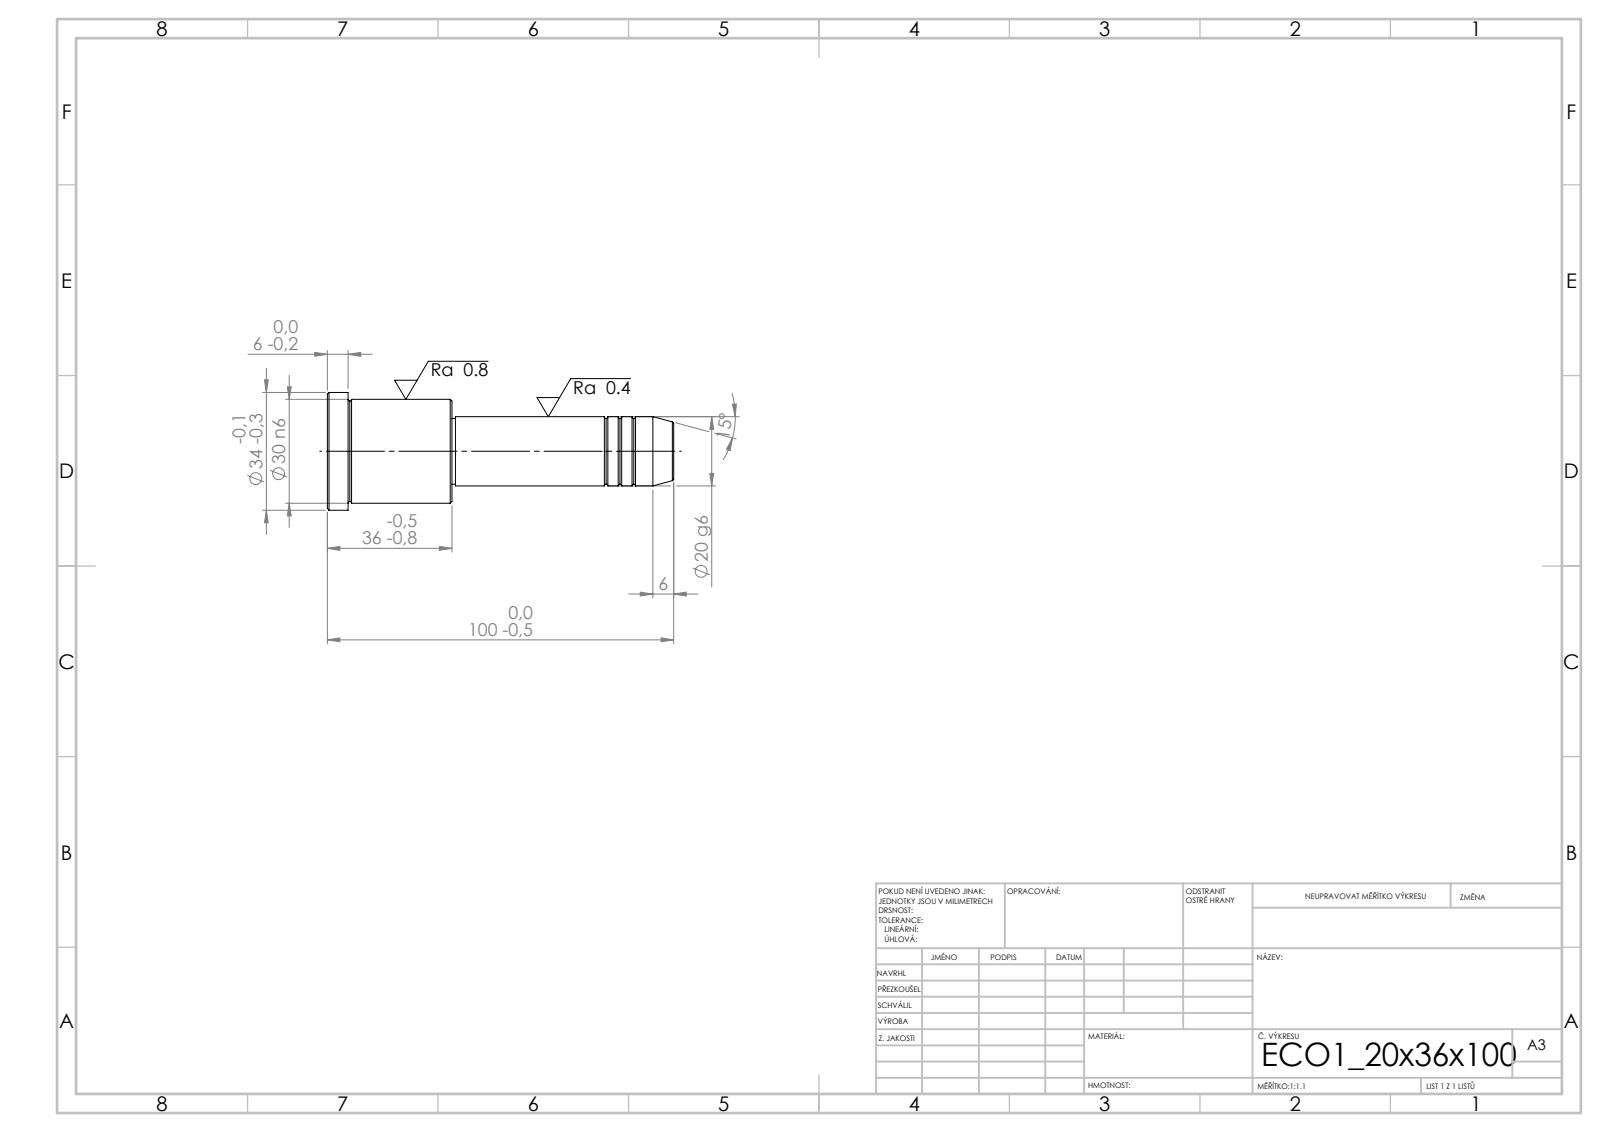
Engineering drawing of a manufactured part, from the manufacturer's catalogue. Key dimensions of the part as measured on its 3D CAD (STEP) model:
STEP written by: SolidWorks 2019 (CONFIG_CONTROL_DESIGN)
Units: millimetres
Bodies: 1 solid, 43 faces (5 planar, 14 cylindrical, 24 other)
Overall size (bounding box): 100 × 34 × 34
Volume: 46 307 mm³ · Surface area: 9 336 mm²
Round bosses / shafts (diameter × count): ⌀34 ×1, ⌀30 ×1, ⌀20 ×1, ⌀19 ×1
Main face-to-face distances: 36, 64, 100, 94, 30, 6, 63, 1, 31, 37
